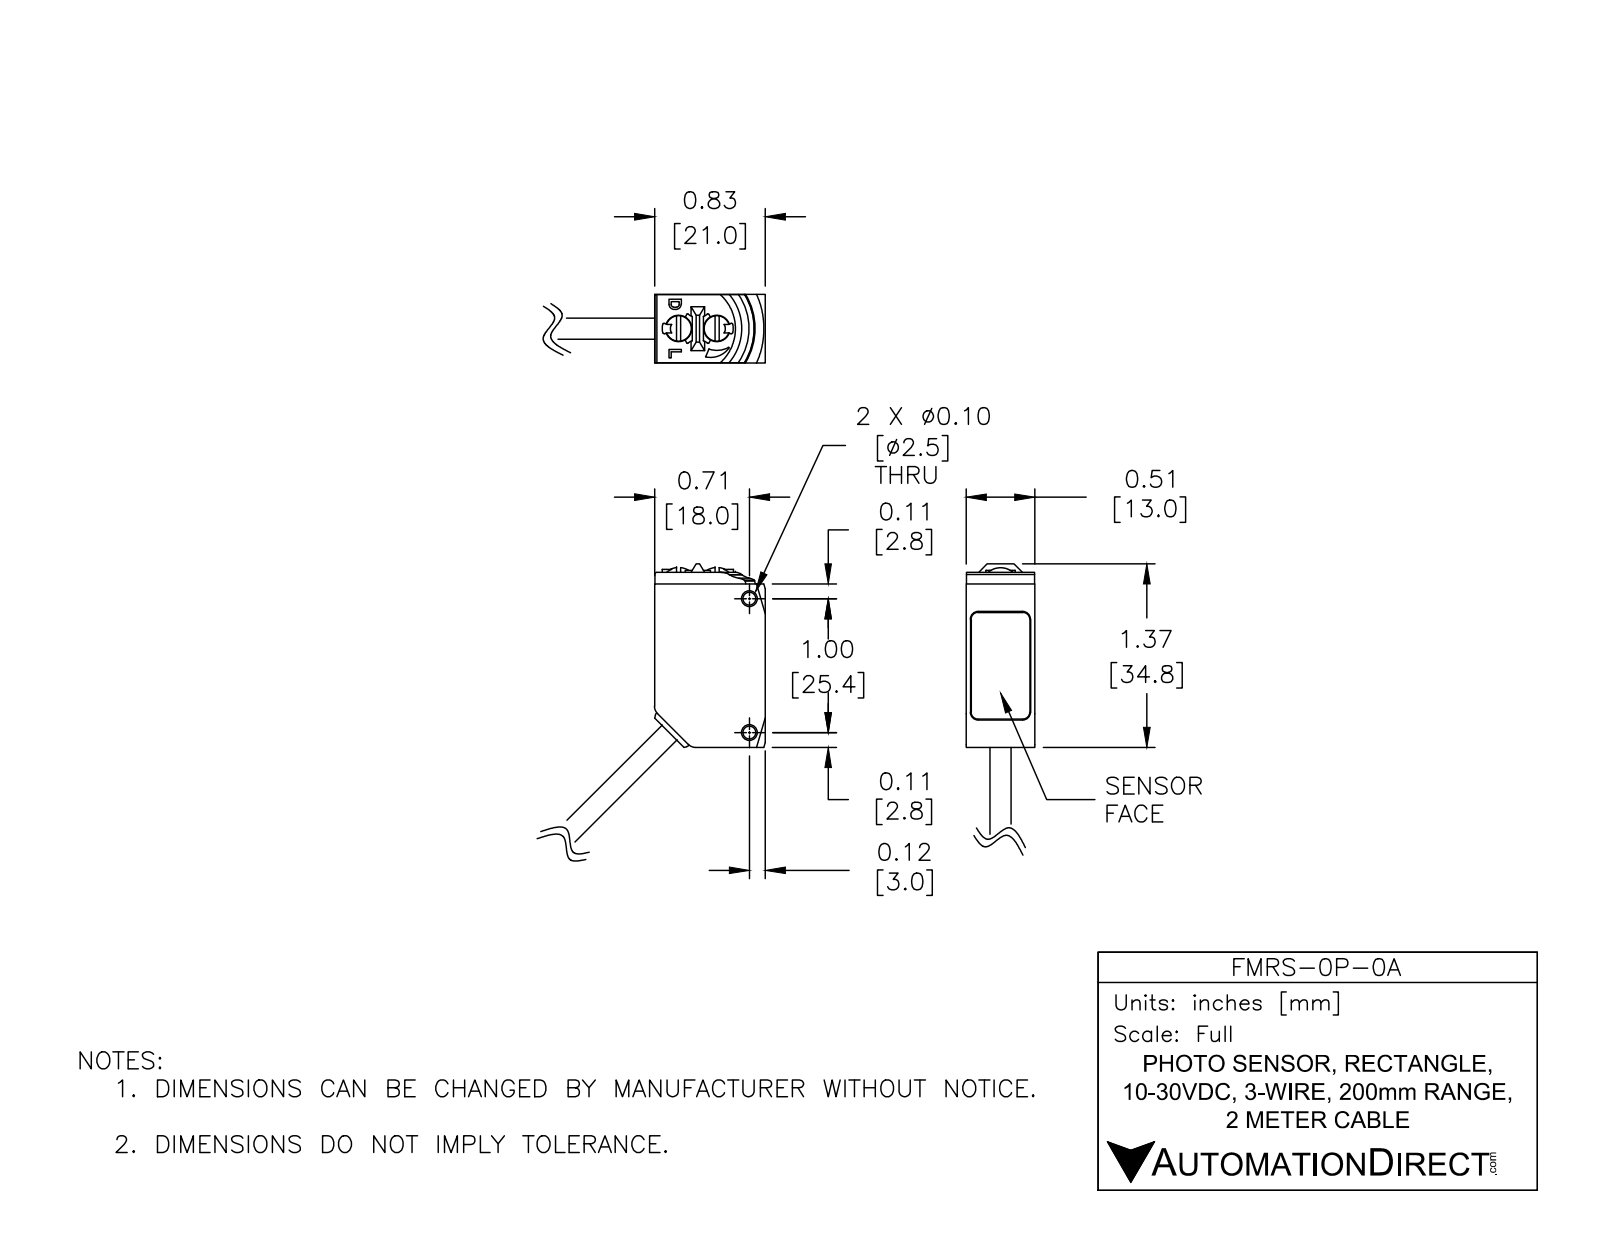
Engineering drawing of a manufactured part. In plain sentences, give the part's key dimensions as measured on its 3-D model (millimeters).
The part is named "FMRS-0P-0A". Its 3-D file was written by "SolidWorks 2017 (AUTOMOTIVE_DESIGN)". It is 1 solid with 186 faces: 89 planar, 72 cylindrical and 25 other. Overall it measures 52.9 by 39.1 by 13 millimeters. Its volume is 8 880 cubic millimeters and its surface area 3 533 square millimeters. Round holes: 2 of diameter 2.5, 2 of diameter 5. Round bosses or shafts: 2 of diameter 4.8, 1 of diameter 4. Partial cylindrical surfaces (rounded edges, fillets, slot ends): 7 of radius 0.5, 7 of radius 0.5, 4 of radius 0.2, 4 of radius 0.3, 4 of radius 1.3, 4 of radius 1.5, 3 of radius 0.1, 2 of radius 0.5. The main face-to-face distances are 13, 21, 33.2, 0.9, 13, 0.8, 12.2, 0.9, 12, 12. The hole center spacings are 7.3, 25.4.
